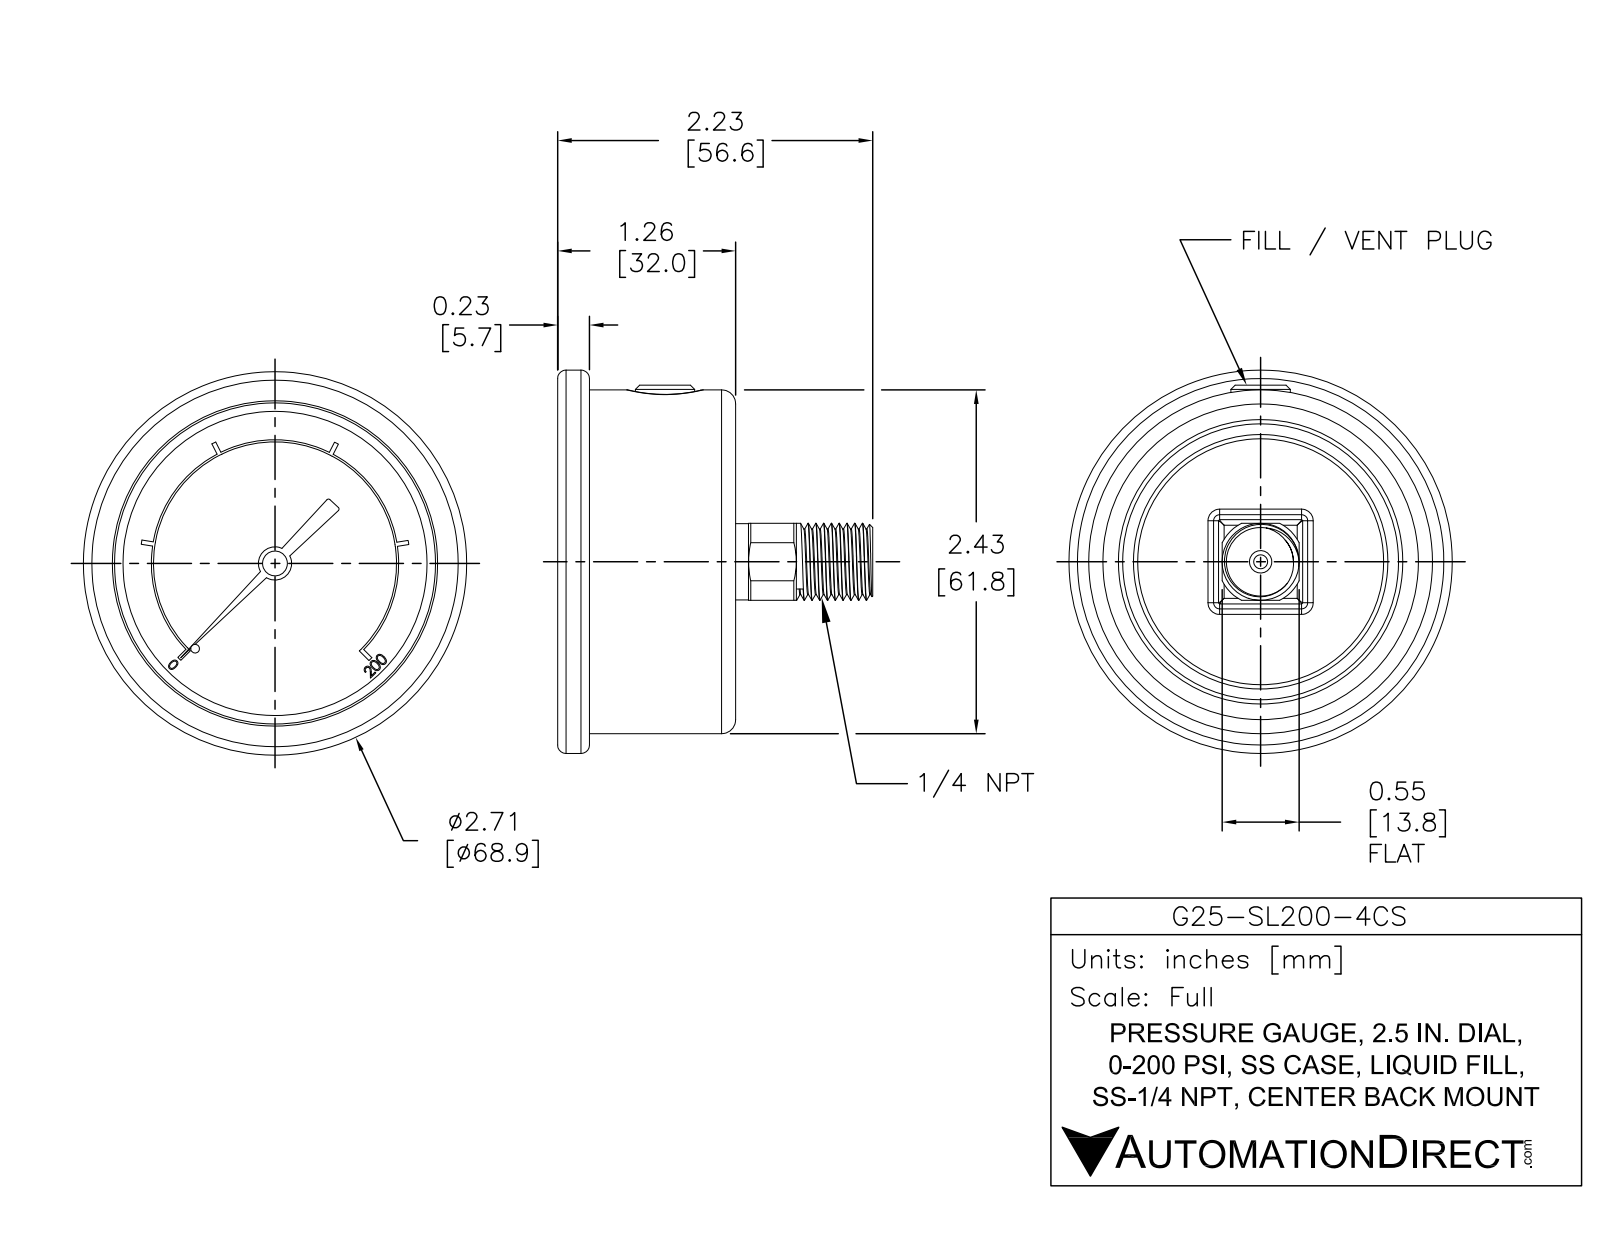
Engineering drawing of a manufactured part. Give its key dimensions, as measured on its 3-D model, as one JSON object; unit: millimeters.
{"part_name": "G25-SL200-4CS", "step_written_by": "SolidWorks 2021 (AUTOMOTIVE_DESIGN)", "units": "millimeters", "bodies": {"solids": 1, "faces": 354, "planar": 208, "cylindrical": 83, "other": 63}, "overall_size": [68.9, 68.9, 56.6], "volume_mm3": 84690, "surface_area_mm2": 16020, "round_holes": [[1.8, 1], [2.5, 1], [57.7, 1]], "round_bosses_or_shafts": [[68.9, 1], [61.8, 1], [13.8, 1], [13.7, 1], [10.7, 1], [6, 1], [4.5, 1], [3.6, 1]], "partial_cylinders_radius": [[1.5, 8], [0.4, 2], [7.7, 1], [21.8, 1], [22.2, 1]], "face_to_face_distances": [24.1, 30.5, 6.4, 1.5, 25.7, 32, 26.3, 24.8, 0.6, 5.7]}
